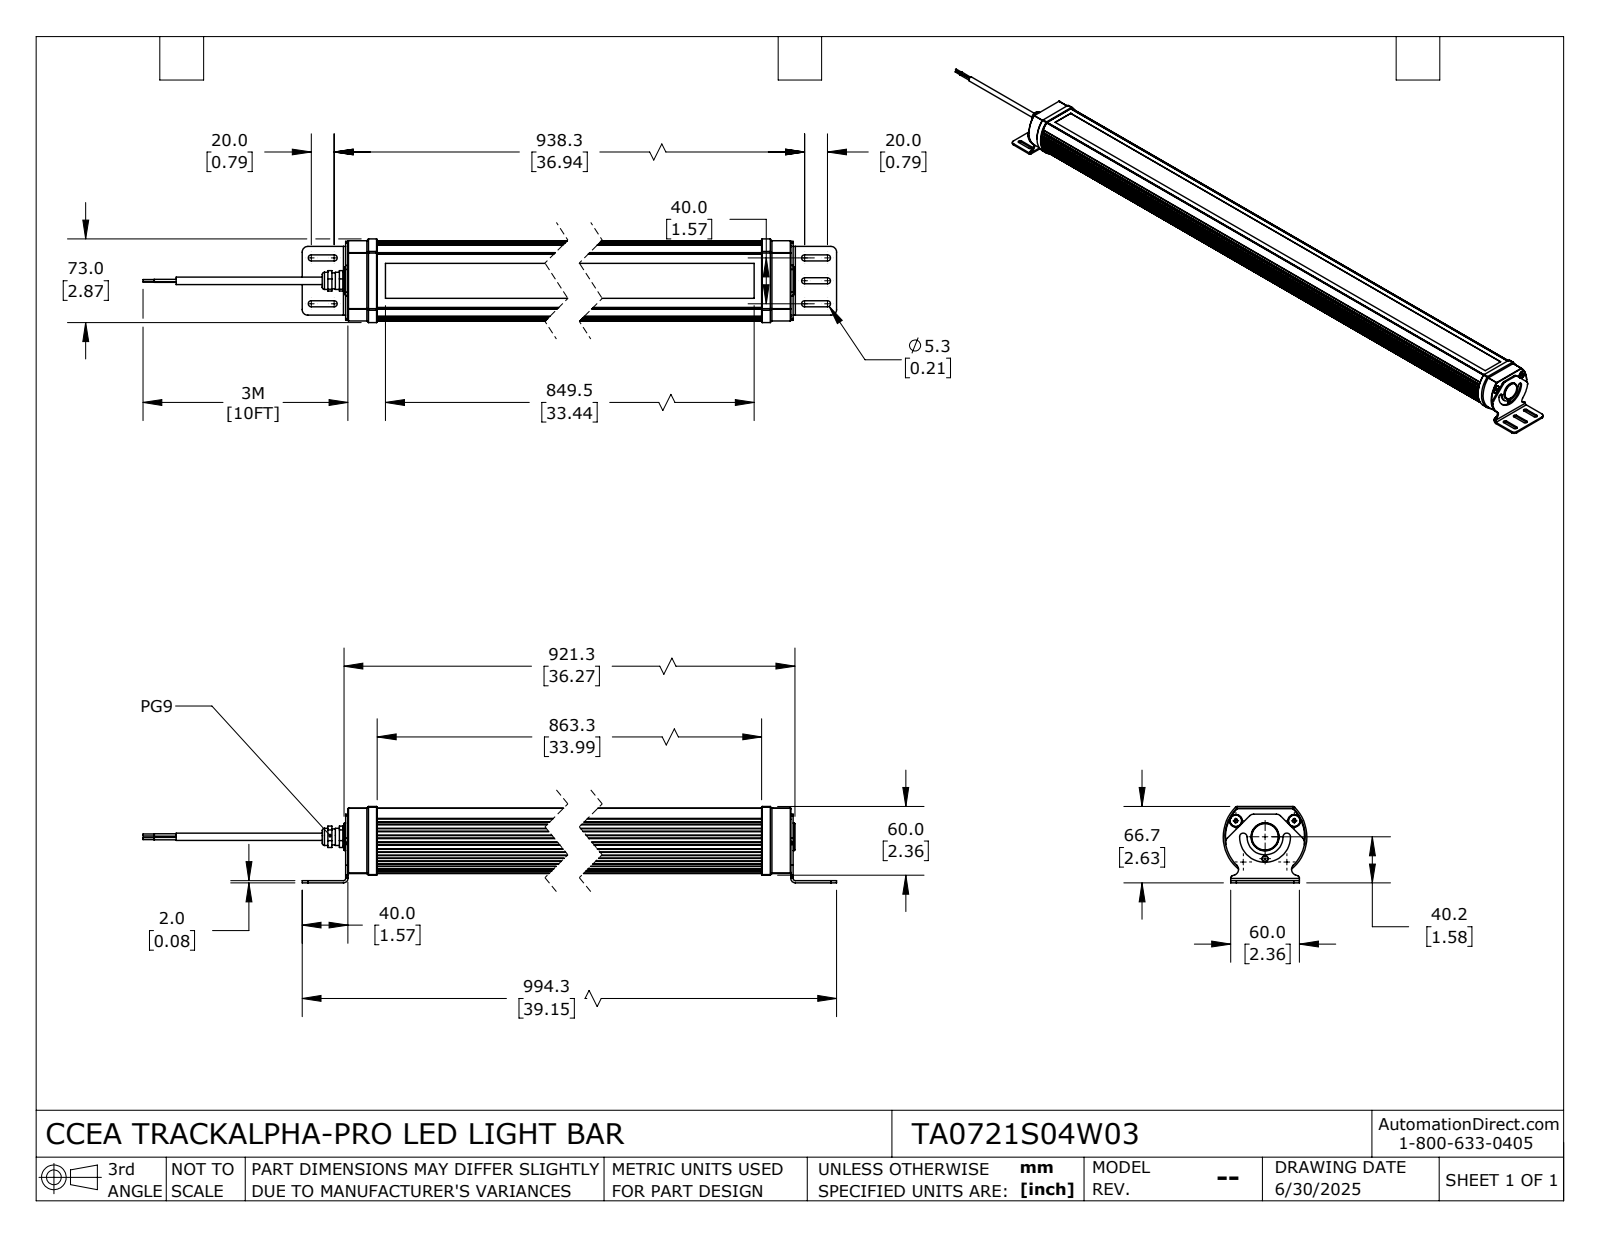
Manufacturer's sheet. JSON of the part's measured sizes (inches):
{"part_name": "TA0721S04W03", "step_written_by": "SolidWorks 2024 (CONFIG_CONTROL_DESIGN)", "units": "inches", "bodies": {"solids": 3, "faces": 695, "planar": 238, "cylindrical": 331, "other": 126}, "overall_size": [44.618, 2.874, 2.626], "volume_in3": 189.6, "surface_area_in2": 474.1, "round_holes": [[0.217, 4], [0.043, 2], [0.12, 2], [0.394, 2], [0.194, 1], [0.276, 1], [0.551, 1], [0.965, 1], [1.063, 1]], "round_bosses_or_shafts": [[0.394, 4], [0.197, 4], [0.118, 2], [0.082, 2], [0.067, 2], [0.063, 2], [0.039, 2], [0.945, 1]], "partial_cylinders_radius": [[0.02, 22], [0.012, 16], [0.197, 13], [0.104, 12], [0.059, 10], [0.073, 8], [0.079, 8], [0.028, 2]], "face_to_face_distances": [2.24, 2.242, 0.197, 0.02, 2.043, 0.199, 0.217, 2.024, 0.219, 1.841], "hole_center_spacings": [0.334, 0.505, 0.726, 0.757, 0.831, 0.948, 0.992, 1.144]}
